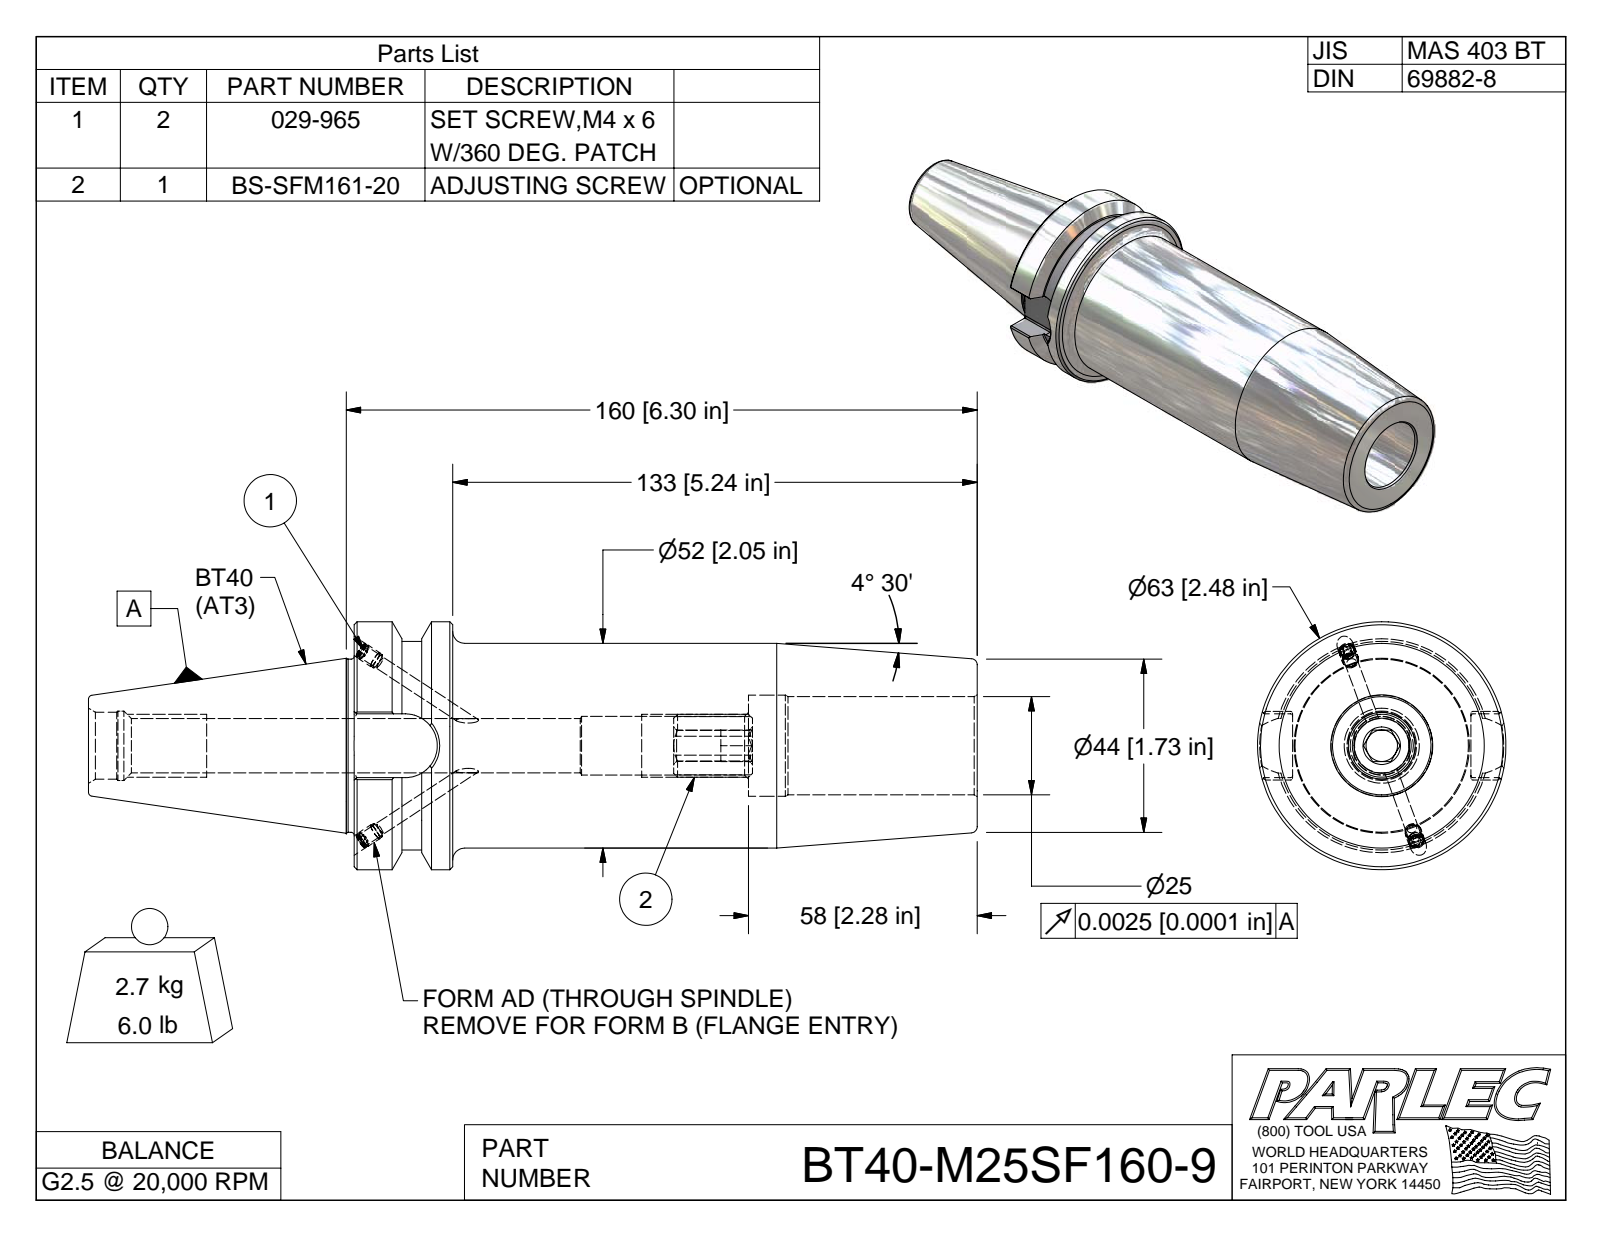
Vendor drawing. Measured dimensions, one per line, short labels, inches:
name: BT40-M25SF160-9; BT40BC-M25SF160-9-1; 029-965; BS-SFM161-20
written by: Autodesk Inventor 2009 (AUTOMOTIVE_DESIGN)
unit: in
bodies: 4 solids, 131 faces (57 planar, 33 cylindrical, 41 other)
size: 8.874 × 2.48 × 2.48
volume: 21.21 in³; area: 82.3 in²
holes: 2× ⌀0.13, 2× ⌀0.161, 1× ⌀0.694, 1× ⌀0.983, 1× ⌀1.013
bosses: 2× ⌀0.165, 2× ⌀0.157, 1× ⌀2.48, 1× ⌀2.087, 1× ⌀2.047, 1× ⌀1.75, 1× ⌀1.73
rounds: 8× R0.02, 1× R0.315, 1× R0.319
face distances: 6.221, 0.984, 5.237, 0.615, 1.166, 3.938, 2.954, 2.283, 1.78, 2.653
